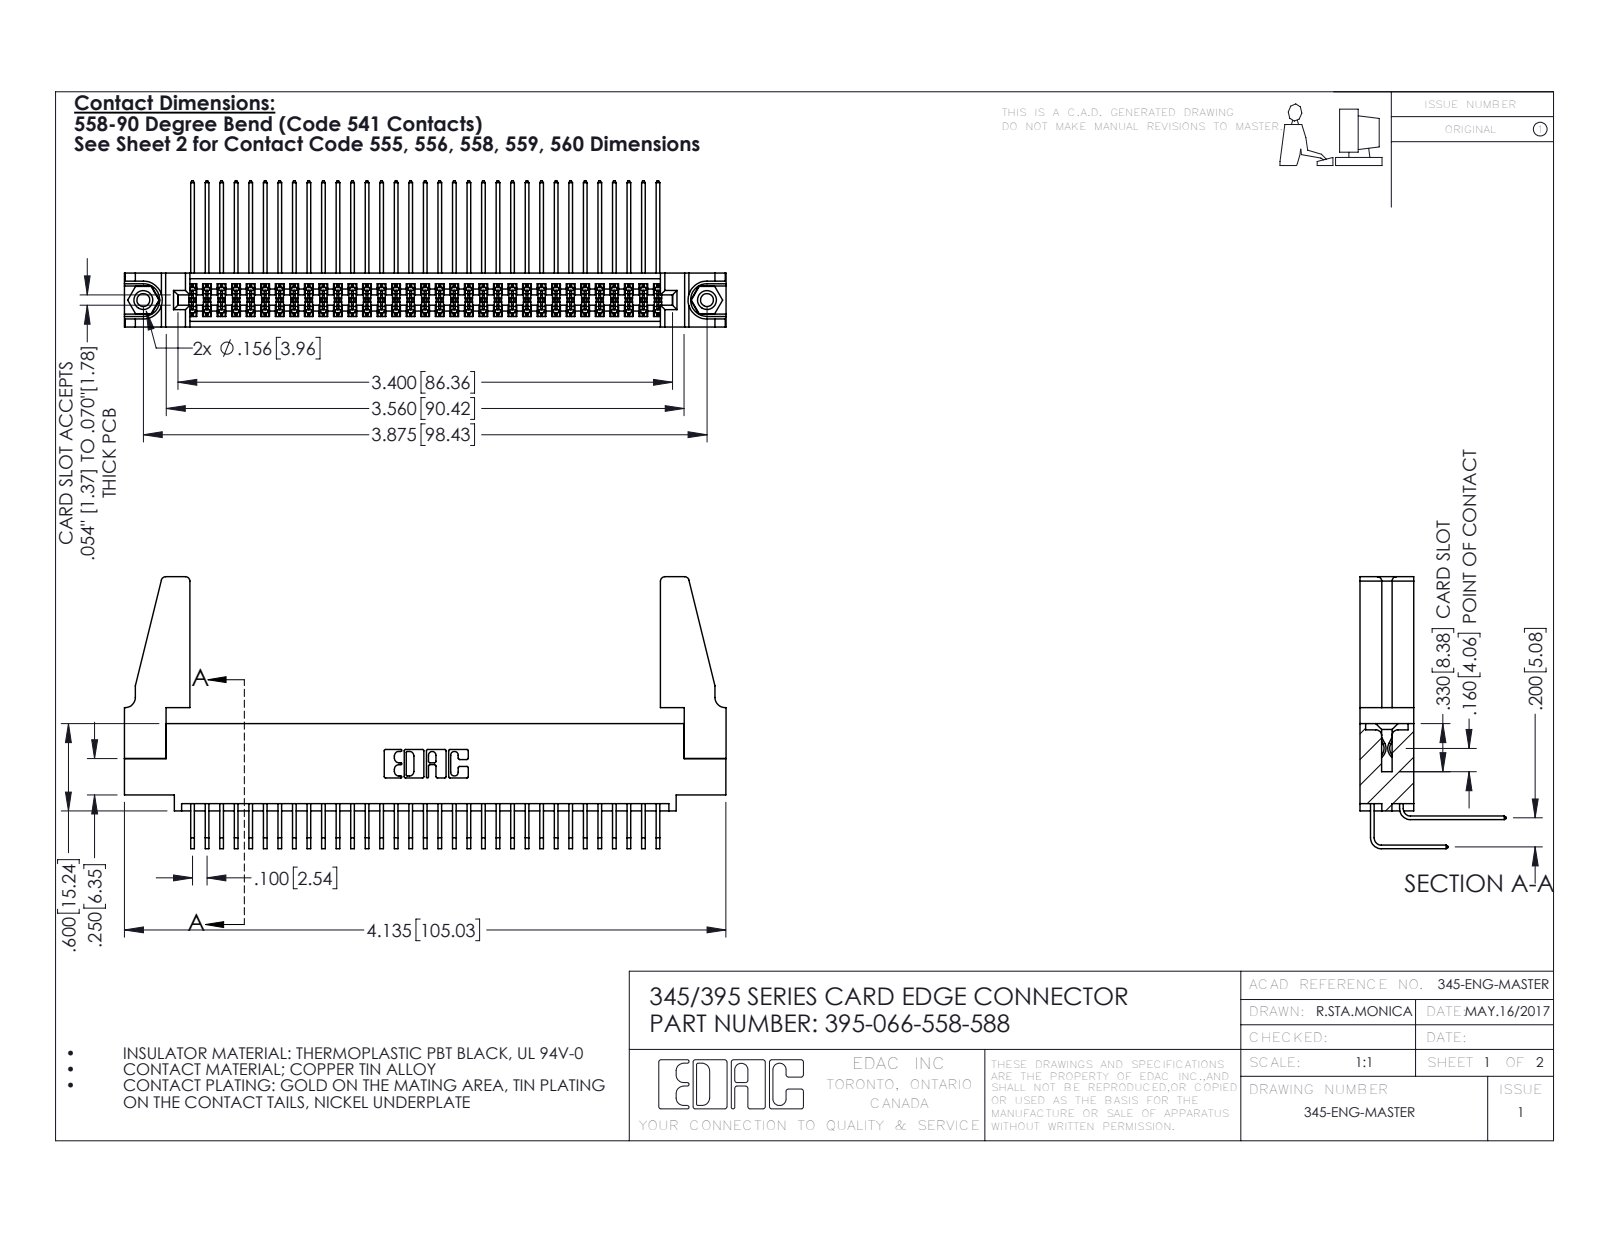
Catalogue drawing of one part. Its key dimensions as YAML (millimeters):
part_name: "345 Part_0.110 Offset - 0.156 Dia-TH; 345-292-001_558 Tail - 2; 345-250-001_345-250-001-102; 395-066-558-588 (+2 more)"
step_written_by: "SolidWorks 2016 (CONFIG_CONTROL_DESIGN)"
units: millimeters
bodies: {solids: 71, faces: 3686, planar: 2466, cylindrical: 1204, other: 16}
overall_size: [105.1, 47.5, 25.5]
volume: 13700
surface_area: 20250
round_holes:
  - {diameter: 2.3, count: 2}
  - {diameter: 3.2, count: 2}
  - {diameter: 4, count: 2}
  - {diameter: 1.6, count: 1}
round_bosses_or_shafts:
  - {diameter: 3.9, count: 2}
partial_cylinders:
  - {radius: 0.2, count: 100}
  - {radius: 0.3, count: 22}
  - {radius: 0.8, count: 8}
  - {radius: 0.2, count: 6}
  - {radius: 0.8, count: 6}
  - {radius: 0.7, count: 3}
  - {radius: 0.4, count: 2}
  - {radius: 0.5, count: 2}
face_to_face_distances: [1.8, 7.6, 9.4, 5.1, 2.5, 6.9, 0.6, 5.7, 0.6, 4.4]
hole_center_spacings: [6.9, 92.5, 98.4]
